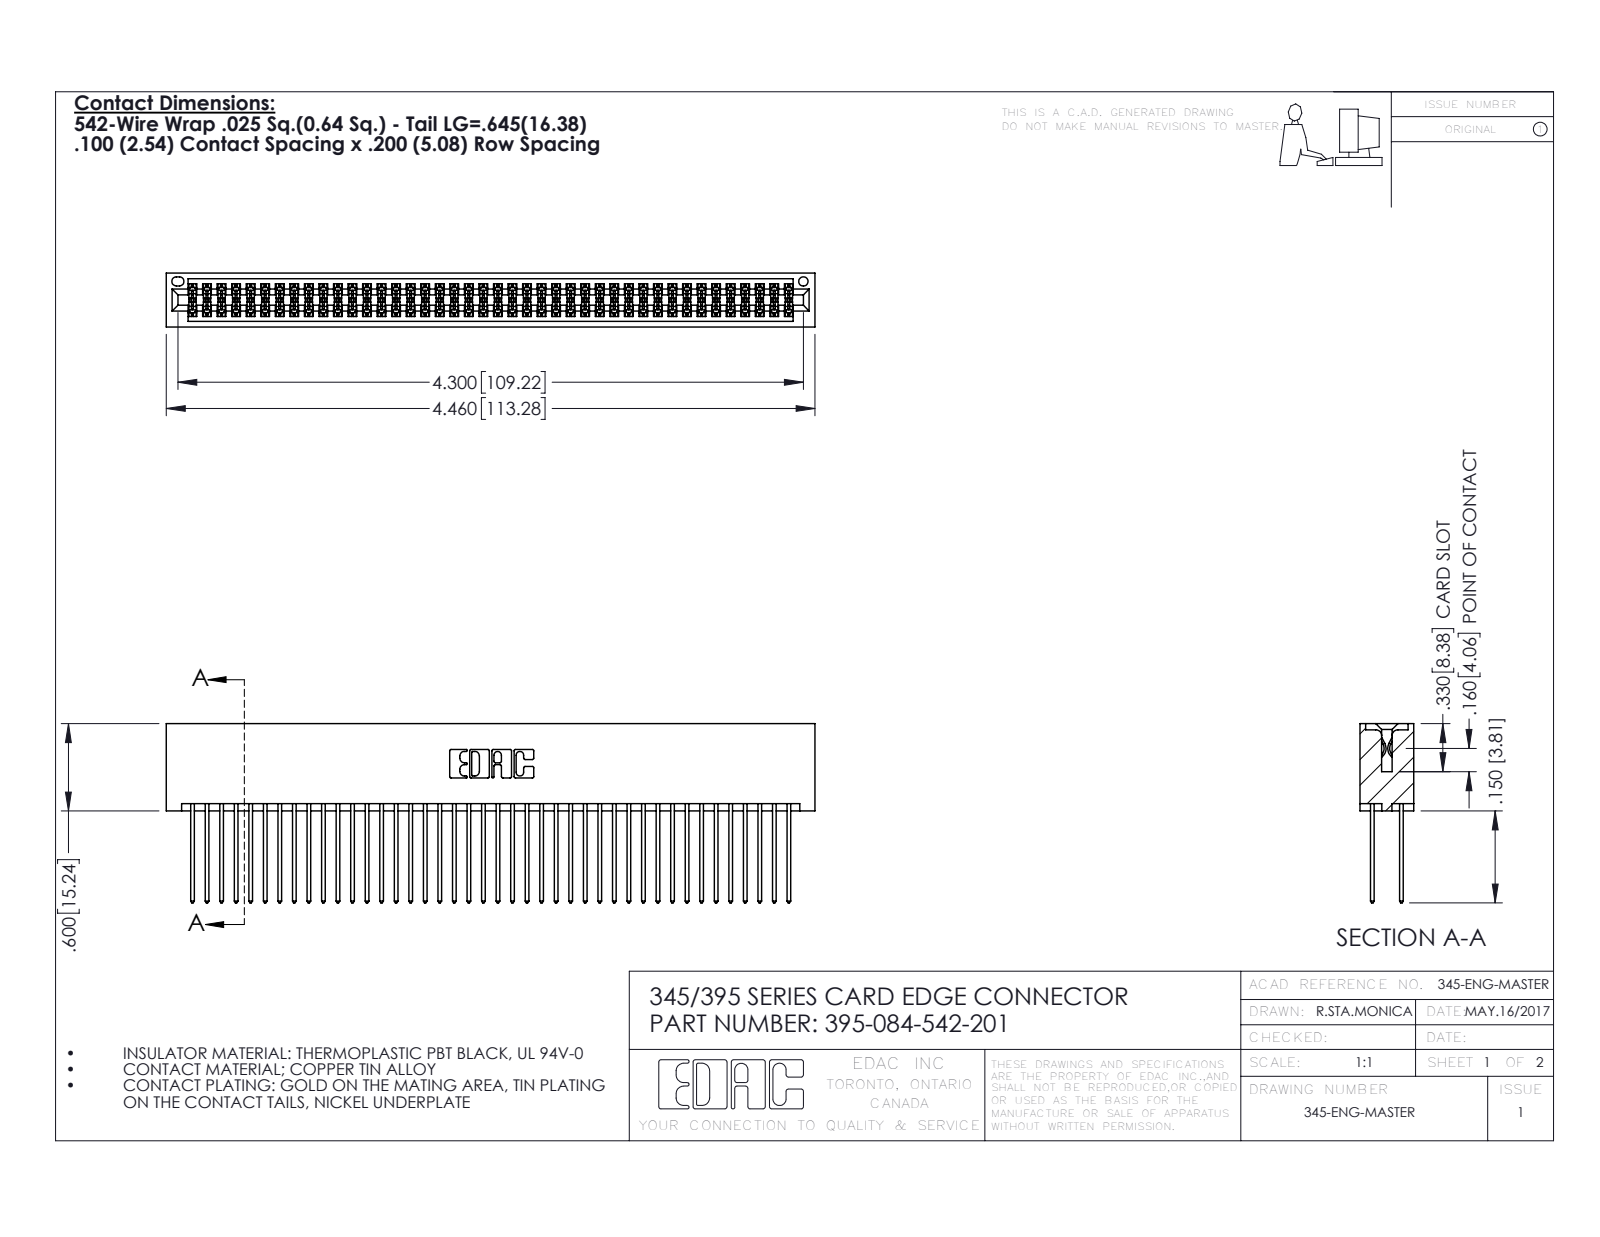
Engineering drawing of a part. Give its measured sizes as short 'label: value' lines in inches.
name: 345 Part_No Mounting Lugs; 395-084-542-201; 345-292-001_345-293-142
written by: SolidWorks 2016 (CONFIG_CONTROL_DESIGN)
unit: in
bodies: 85 solids, 4318 faces (2848 planar, 1470 cylindrical, 0 other)
size: 4.46 × 1.232 × 0.37
volume: 0.733 in³; area: 30.83 in²
holes: 1× ⌀0.064
rounds: 126× R0.006, 84× R0.01, 22× R0.01, 6× R0.007, 6× R0.031, 3× R0.026, 2× R0.014, 2× R0.019
face distances: 0.298, 0.072, 0.2, 0.098, 0.272, 0.025, 0.225, 0.37, 0.175, 0.149
